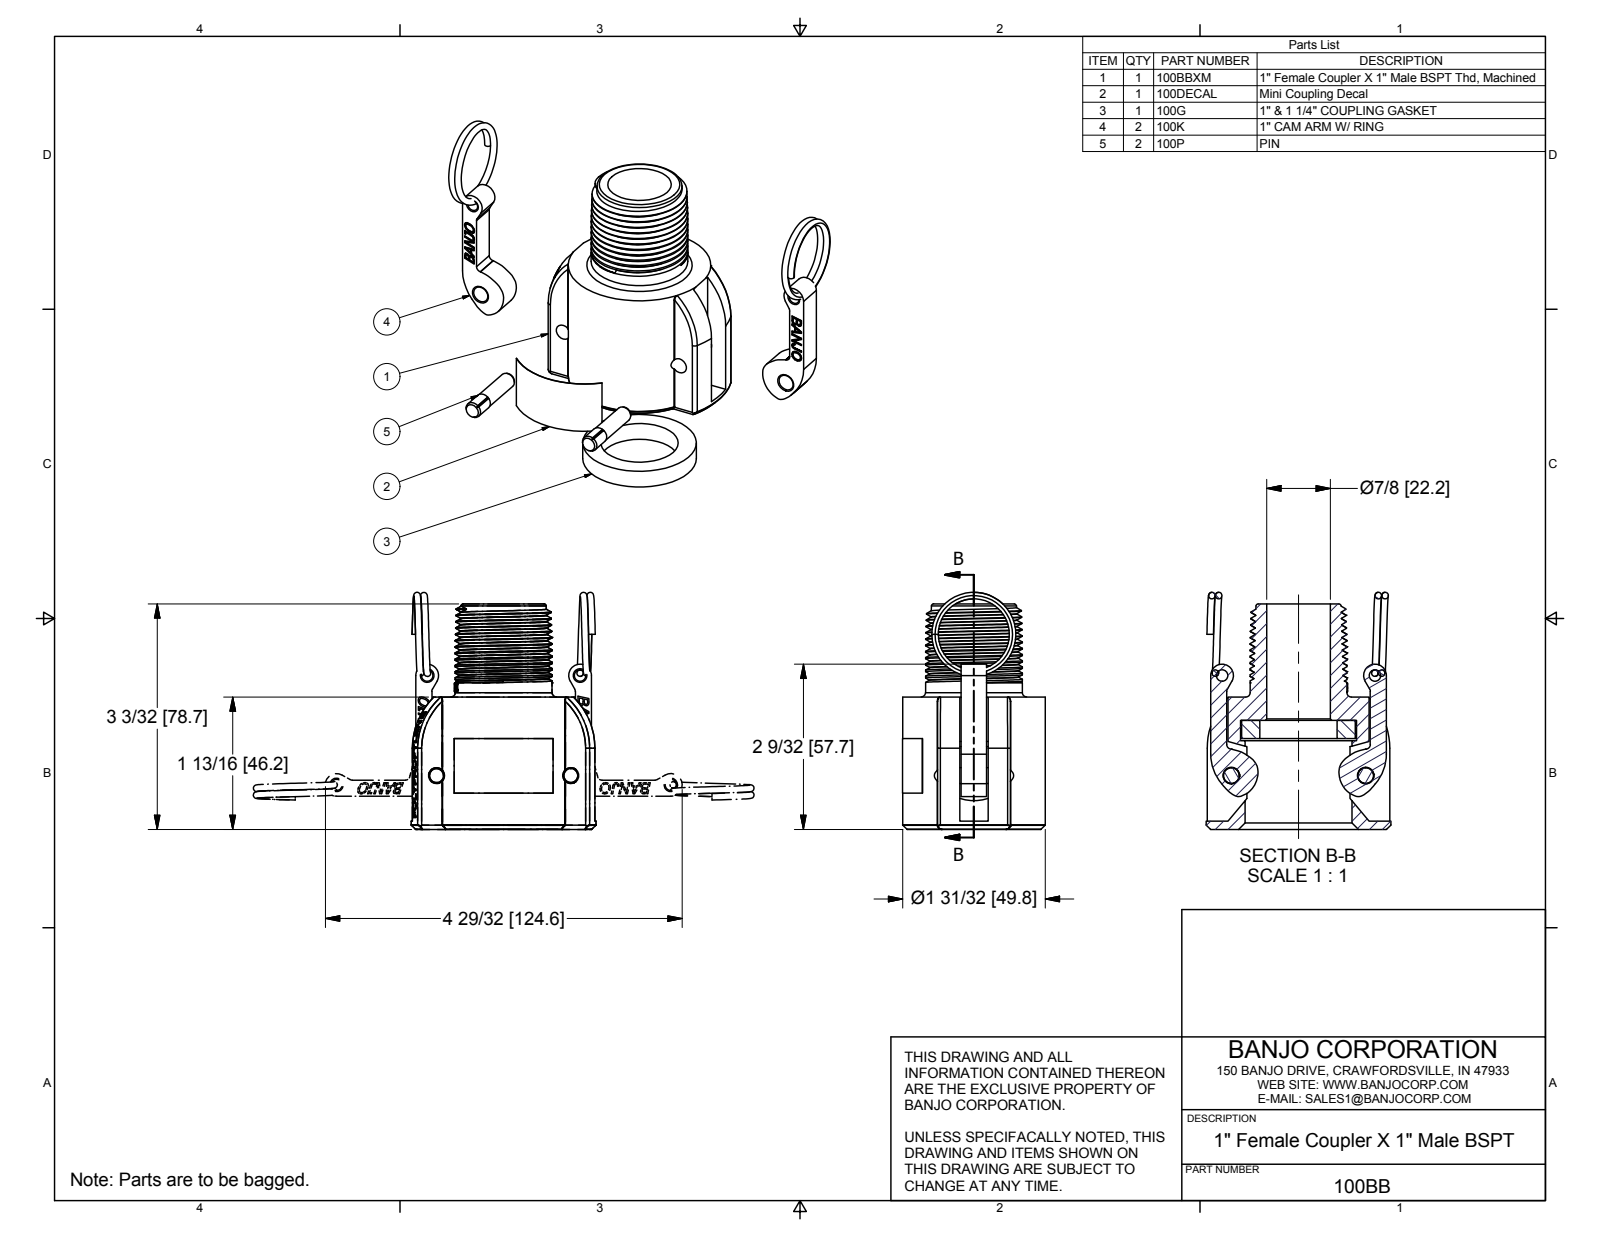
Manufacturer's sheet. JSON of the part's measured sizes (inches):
{"part_name": "100BBX; 100BBXM; 100G; 100P (+6 more)", "step_written_by": "Autodesk Inventor 2014 (AUTOMOTIVE_DESIGN)", "units": "inches", "bodies": {"solids": 9, "faces": 901, "planar": 430, "cylindrical": 92, "other": 379}, "overall_size": [3.259, 2.54, 1.963], "volume_in3": 4.676, "surface_area_in2": 58.21, "round_holes": [[0.156, 2], [0.219, 2], [0.225, 2], [0.875, 1], [1.063, 1], [1.47, 1], [1.594, 1]], "round_bosses_or_shafts": [[0.227, 2], [0.217, 2], [1.563, 1], [1.33, 1]], "partial_cylinders_radius": [[0.06, 6], [0.01, 4], [0.063, 2], [0.063, 2], [0.156, 2], [0.625, 2], [0.359, 1], [0.675, 1]], "face_to_face_distances": [0.305, 0.695, 0.32, 0.39, 0.25, 0.57, 1.25, 1.5, 1.82, 0.022], "hole_center_spacings": [1.381, 1.847, 2.102, 2.406, 2.406]}
